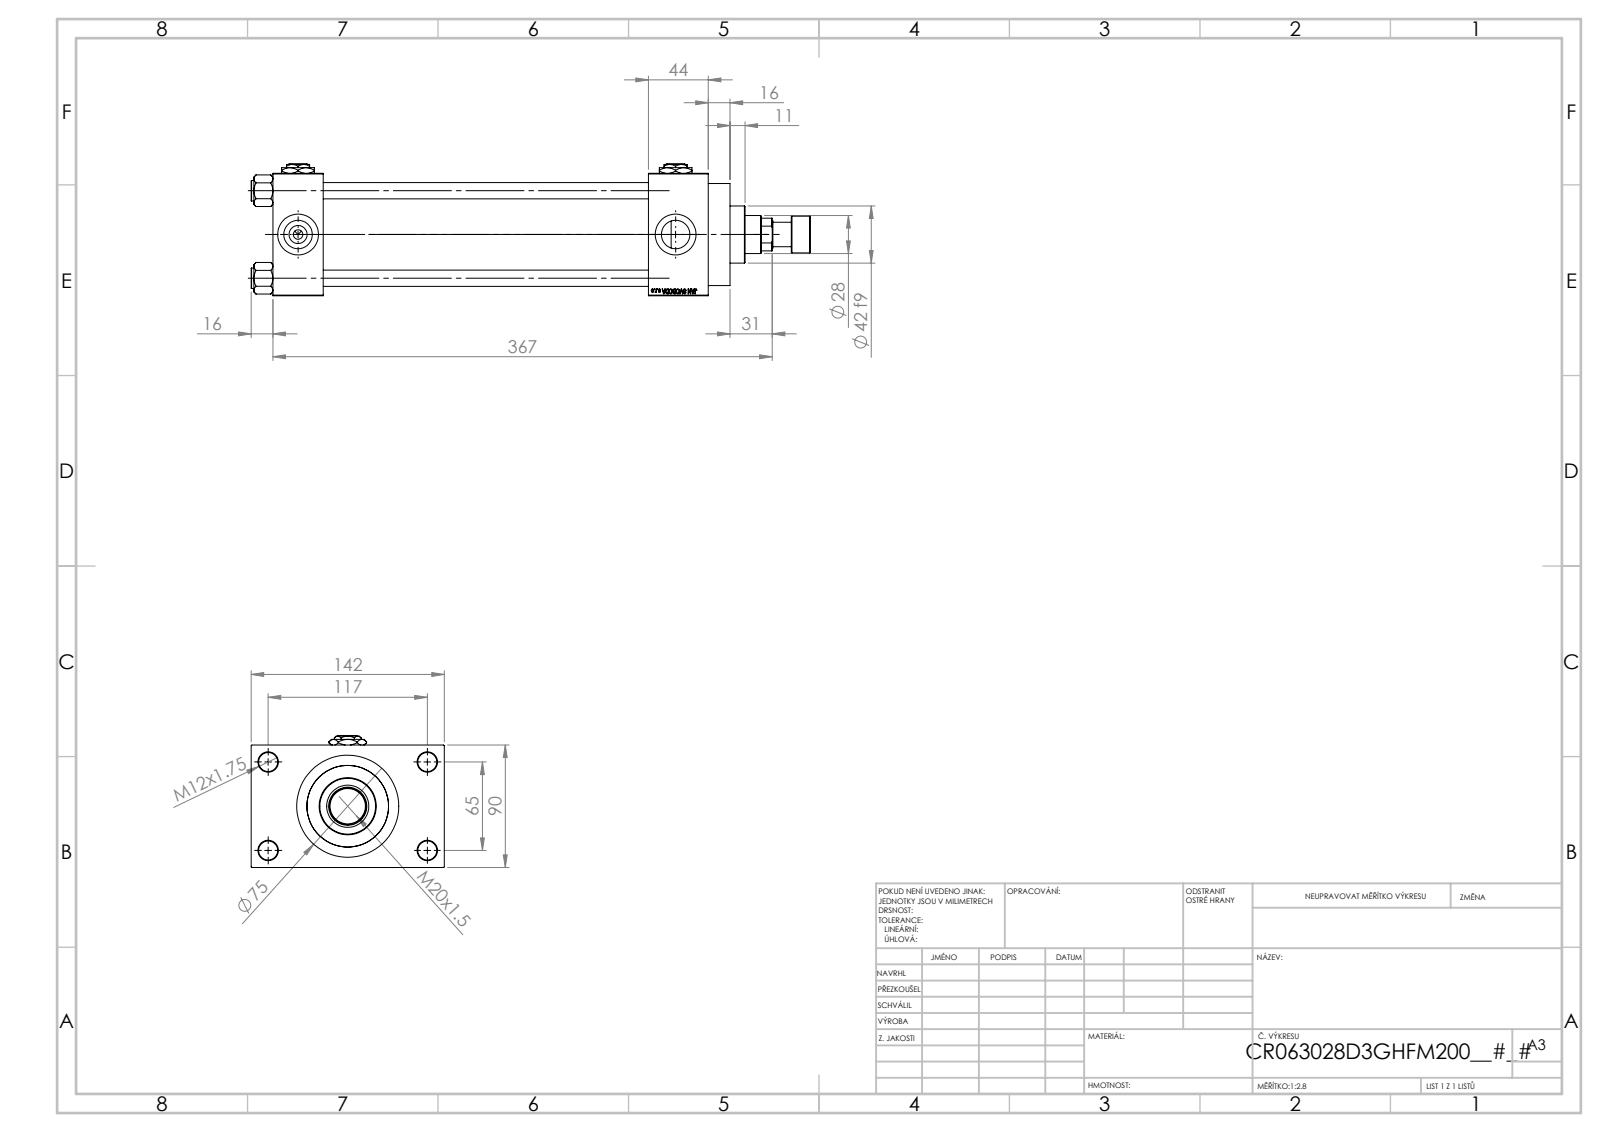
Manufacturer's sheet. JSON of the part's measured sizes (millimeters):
{"part_name": "V215CR_VCP_D; V215CR_ROD_END_F; V215CR_D_TYCINKA; NUT_M5_D (+3 more)", "step_written_by": "SolidWorks 2019 (CONFIG_CONTROL_DESIGN)", "units": "millimeters", "bodies": {"solids": 14, "faces": 1218, "planar": 549, "cylindrical": 103, "other": 566}, "overall_size": [411, 142, 97], "volume_mm3": 1407000, "surface_area_mm2": 325819, "round_holes": [[12, 4], [14, 4], [20.96, 4], [30, 4], [7, 3], [18.5, 1], [28, 1], [31, 1], [50, 1], [60, 1], [63, 1]], "round_bosses_or_shafts": [[15, 4], [75, 1], [69, 1], [42, 1], [27, 1], [18, 1]], "face_to_face_distances": [90, 239, 37, 276, 283, 320, 44, 26, 116, 16], "hole_center_spacings": [26.35, 45.47, 64.3, 66.92, 69.81, 90.65, 111.34, 65]}
